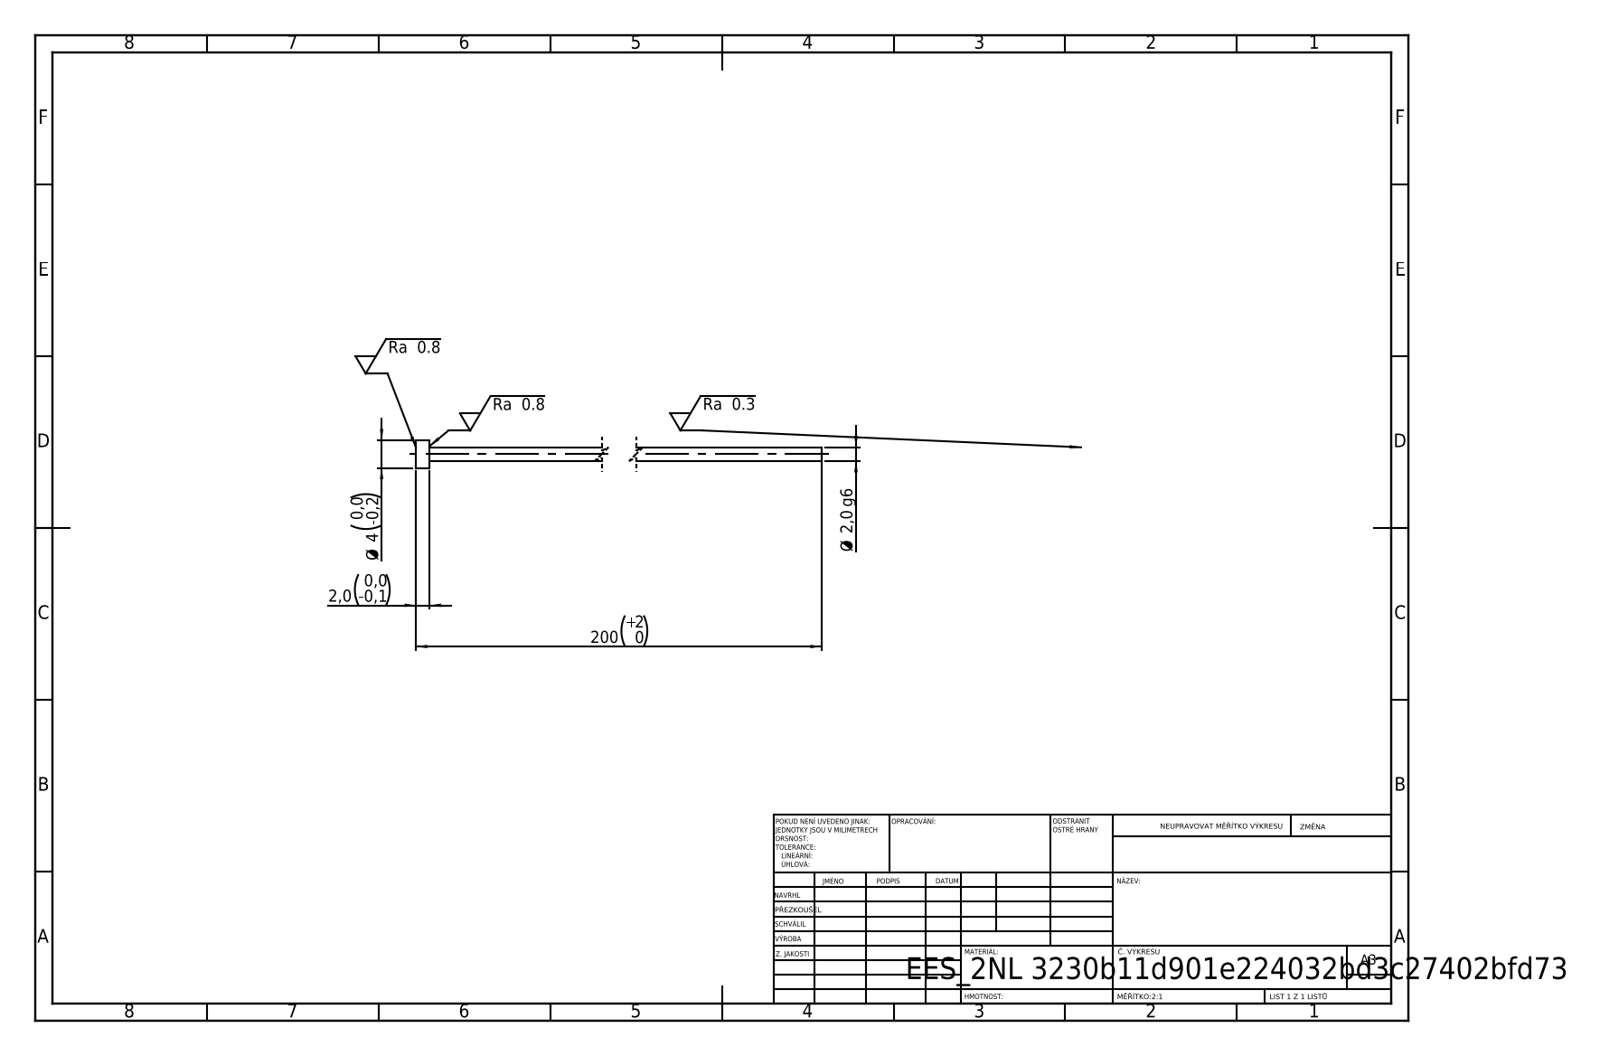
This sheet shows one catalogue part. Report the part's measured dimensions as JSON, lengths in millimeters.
{"step_written_by": "SolidWorks 2019 (CONFIG_CONTROL_DESIGN)", "units": "millimeters", "bodies": {"solids": 1, "faces": 7, "planar": 3, "cylindrical": 4, "other": 0}, "overall_size": [200, 4, 4], "volume_mm3": 647, "surface_area_mm2": 1294, "round_bosses_or_shafts": [[4, 1], [2, 1]], "face_to_face_distances": [2, 200, 198]}
